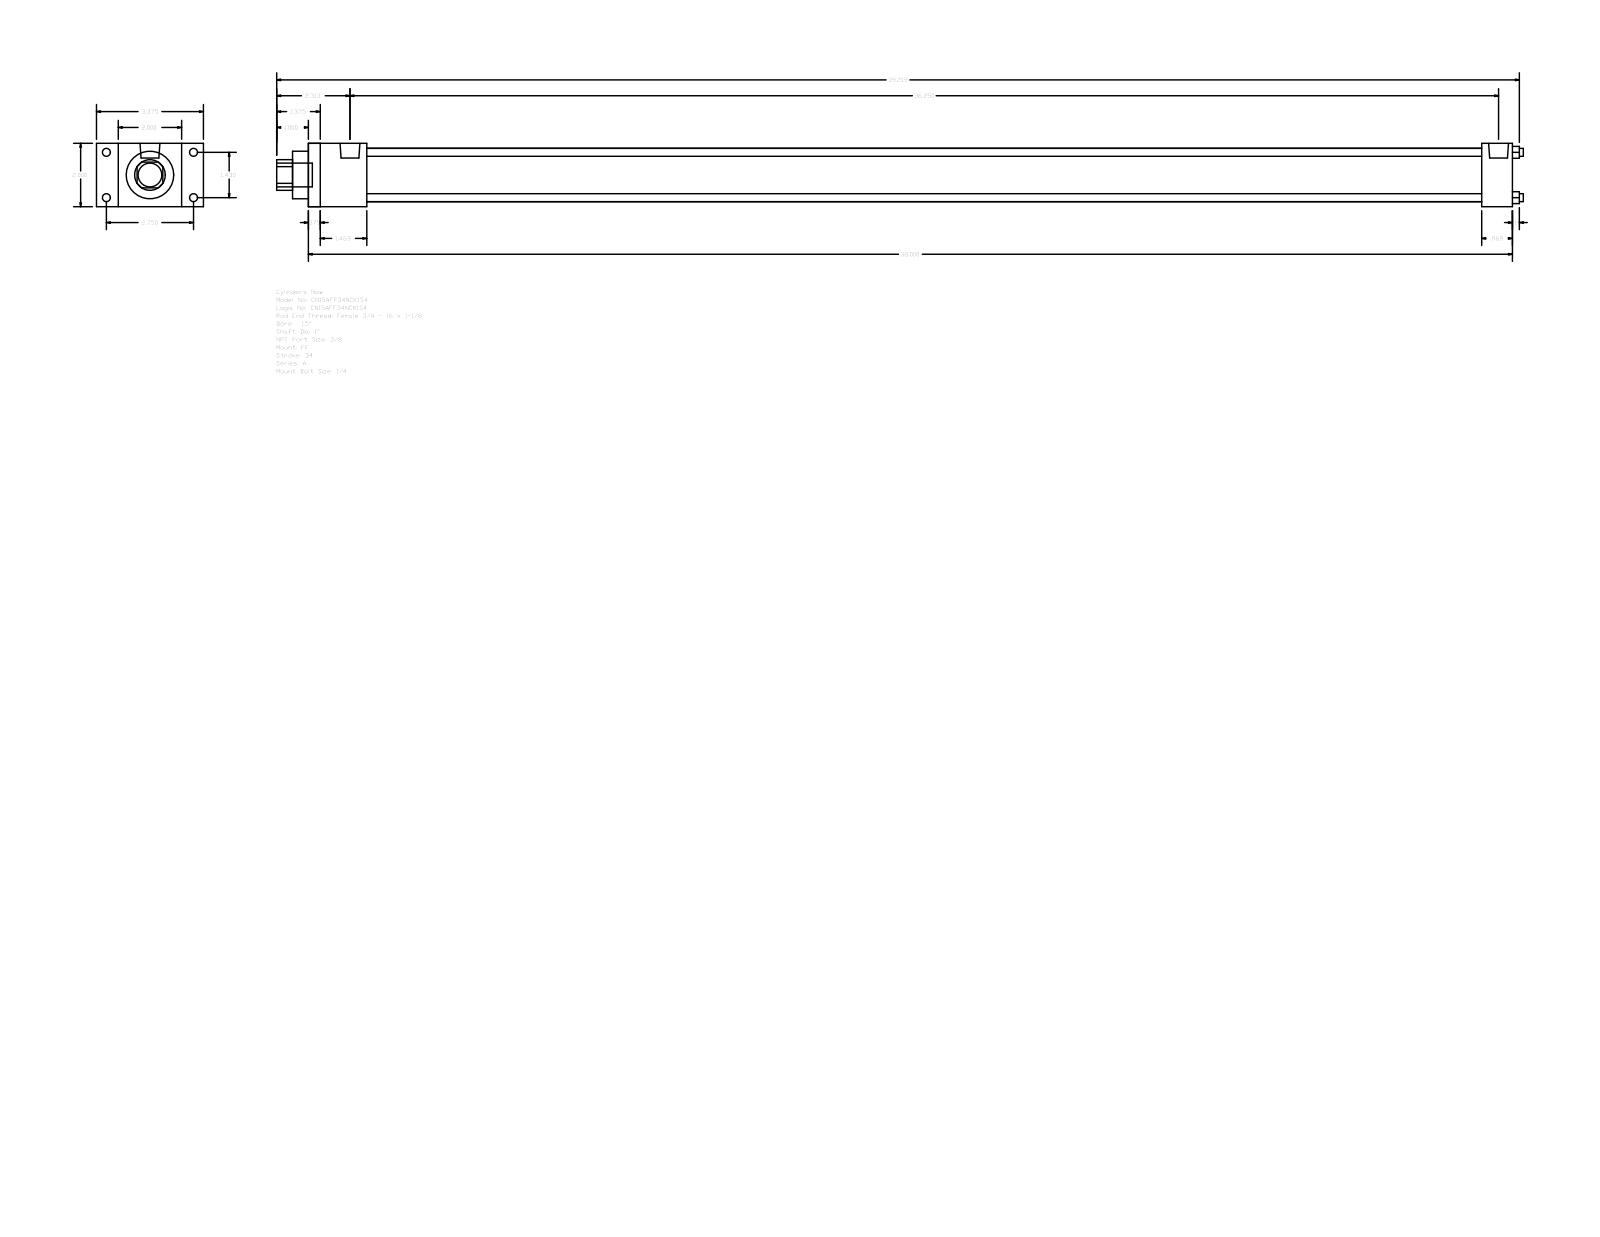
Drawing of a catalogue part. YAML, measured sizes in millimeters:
part_name: "A_FF__0150_1"
step_written_by: "GSSL Pune (CONFIG_CONTROL_DESIGN)"
units: millimeters
bodies: {solids: 0, faces: 92, planar: 64, cylindrical: 28, other: 0}
overall_size: [999.33, 85.72, 50.8]
round_holes:
  - {diameter: 6.35, count: 4}
  - {diameter: 25.4, count: 1}
  - {diameter: 38.1, count: 1}
  - {diameter: 42.93, count: 1}
round_bosses_or_shafts:
  - {diameter: 6.35, count: 4}
  - {diameter: 5.56, count: 4}
  - {diameter: 15.93, count: 2}
  - {diameter: 19.05, count: 1}
partial_cylinders:
  - {radius: 12.29, count: 1}
face_to_face_distances: [50.8, 965.2, 9.52, 955.68, 46.83, 940.59, 37.31, 931.07, 893.76, 918.37]
hole_center_spacings: [25.68, 36.32, 51.36]
